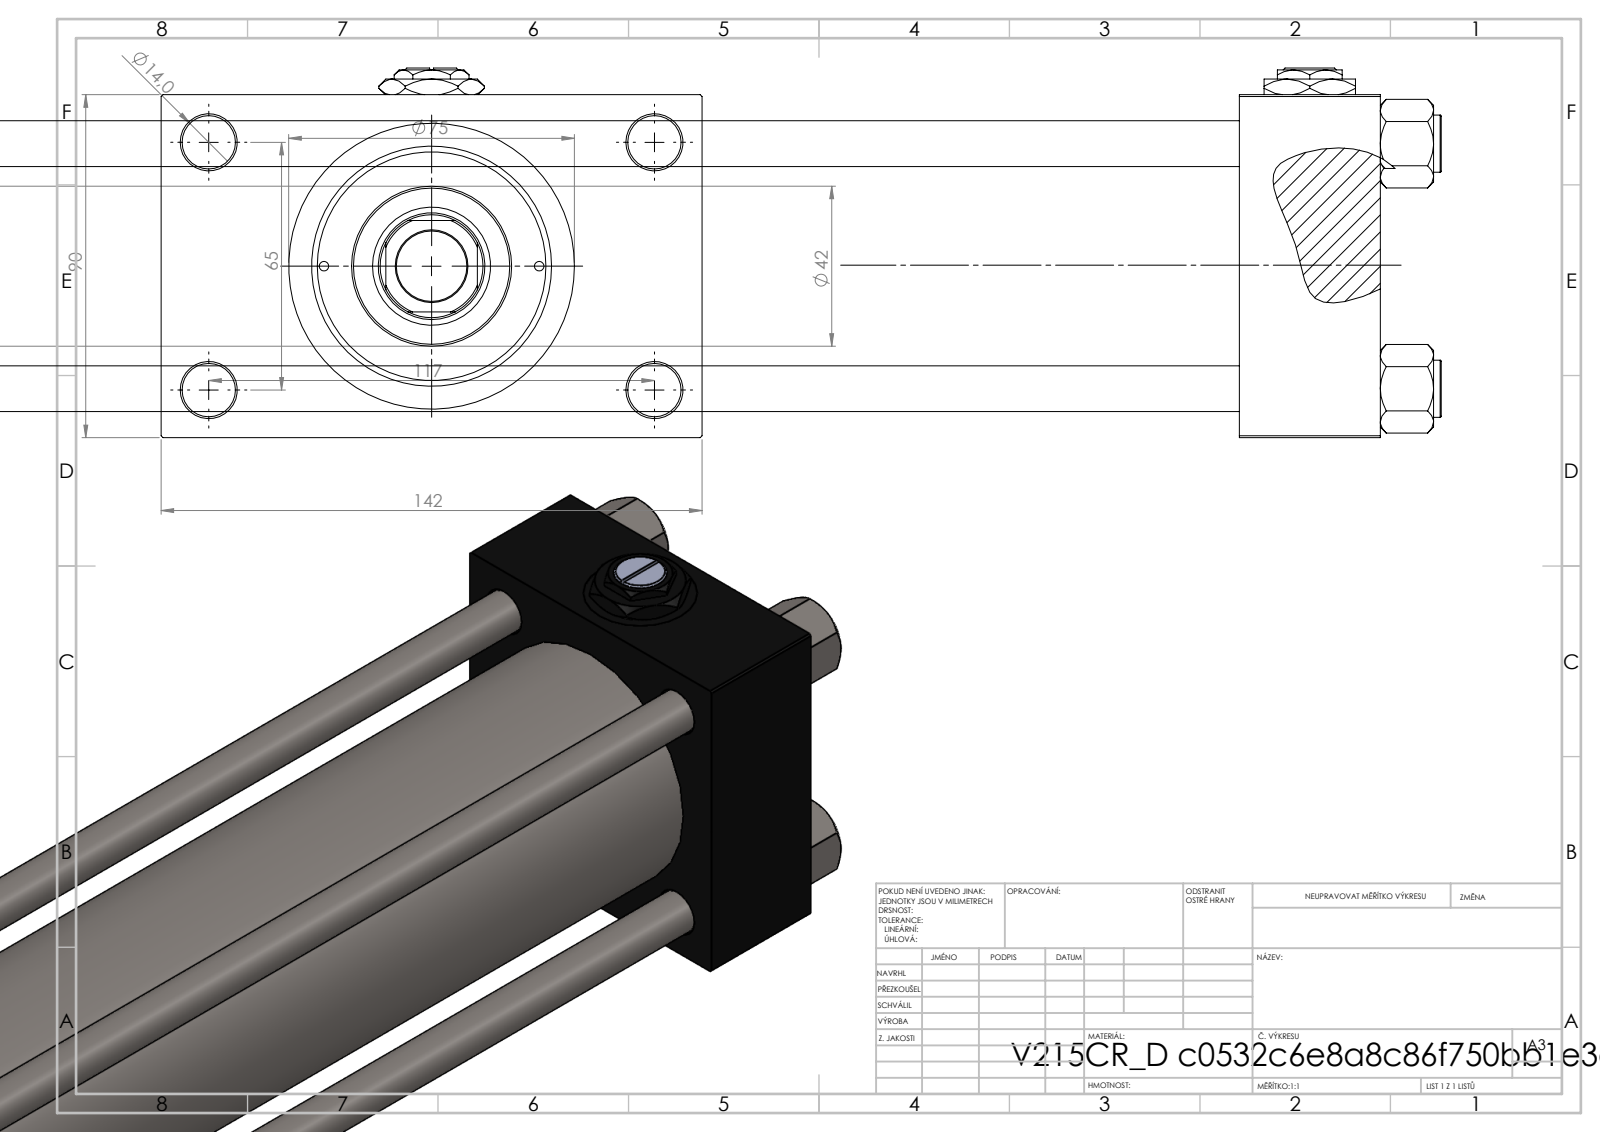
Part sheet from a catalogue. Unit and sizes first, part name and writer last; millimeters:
Units: millimetres
Overall size (bounding box): 883 × 142 × 97
Round holes (diameter × count): ⌀12 ×4, ⌀14 ×4, ⌀2.5 ×2, ⌀7 ×2, ⌀20.96 ×2, ⌀30 ×2, ⌀18.5 ×1, ⌀28 ×1, ⌀31 ×1, ⌀50 ×1, ⌀60 ×1, ⌀63 ×1
Round bosses / shafts (diameter × count): ⌀15 ×4, ⌀75 ×1, ⌀69 ×1, ⌀42 ×1
Partial cylindrical surfaces — rounded edges, fillets, slot ends (radius × count): R13.5 ×1
Main face-to-face distances: 90, 739, 37, 776, 783, 820, 44, 26, 116, 142
Hole centre spacings: 26.35, 32.39, 44.4, 45.47, 64.3, 66.92, 68.42, 69.81
Volume: 2 249 000 mm³ · Surface area: 647 499 mm²
Bodies: 13 solids, 1213 faces (547 planar, 104 cylindrical, 562 other)
Part name (STEP PRODUCT): V215CR_VCP_D; V215CR_D_Body; V215CR_D_TYCINKA; V215_VC_A (+2 more)
STEP written by: SolidWorks 2019 (CONFIG_CONTROL_DESIGN)
